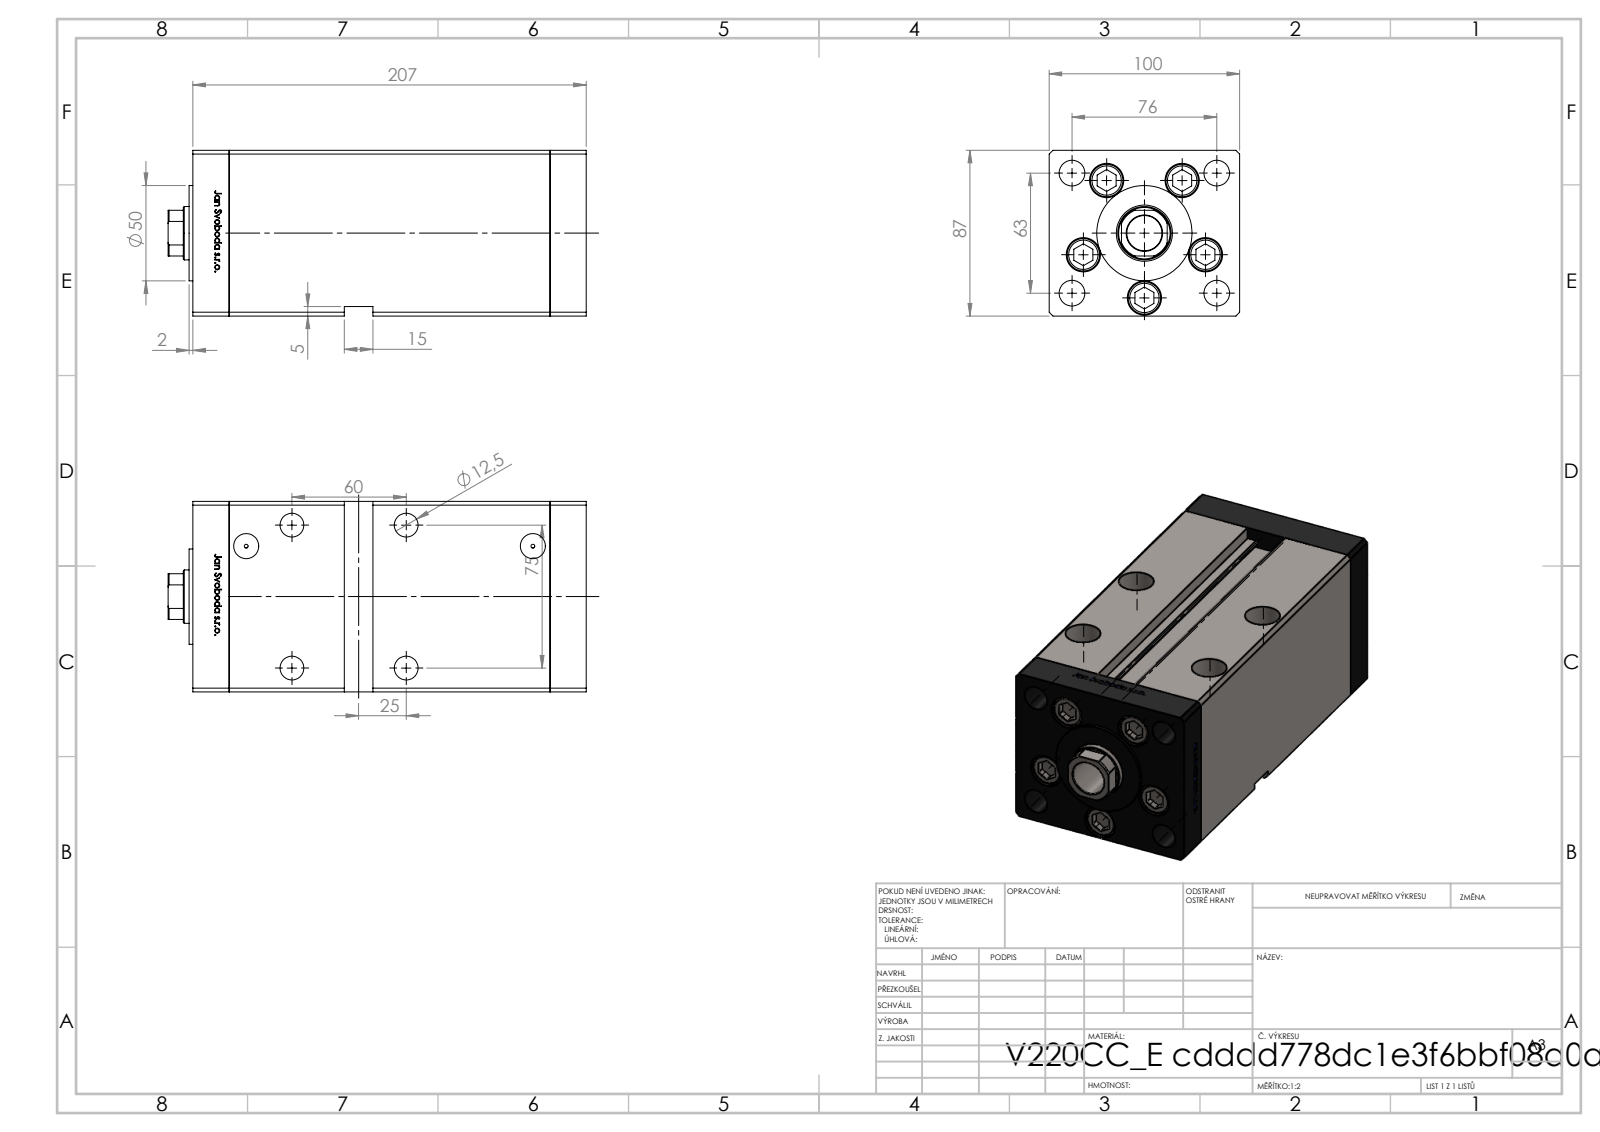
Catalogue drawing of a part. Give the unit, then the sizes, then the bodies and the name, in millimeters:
Units: millimetres
Overall size (bounding box): 219.5 × 100 × 87
Round holes (diameter × count): ⌀13.5 ×11, ⌀18 ×5, ⌀18.5 ×5, ⌀12.5 ×4, ⌀2 ×2, ⌀13.16 ×2, ⌀28 ×1, ⌀29.5 ×1
Round bosses / shafts (diameter × count): ⌀17 ×5, ⌀8 ×5, ⌀50 ×1
Partial cylindrical surfaces — rounded edges, fillets, slot ends (radius × count): R0.93 ×2, R13.5 ×1
Main face-to-face distances: 100, 87, 19, 168.5, 187.5, 34.25, 206.5, 15.25, 153.25, 172.25
Hole centre spacings: 34, 18.59, 39.64, 49.36, 57.95, 21.03, 38.08, 39.27
Volume: 1 508 000 mm³ · Surface area: 233 827 mm²
Bodies: 14 solids, 1214 faces (475 planar, 165 cylindrical, 574 other)
Part name (STEP PRODUCT): V220C BACK_E; V220C_FRONT_E; ALLEN BOLT; V220C_VC_E (+1 more)
STEP written by: SolidWorks 2019 (CONFIG_CONTROL_DESIGN)
